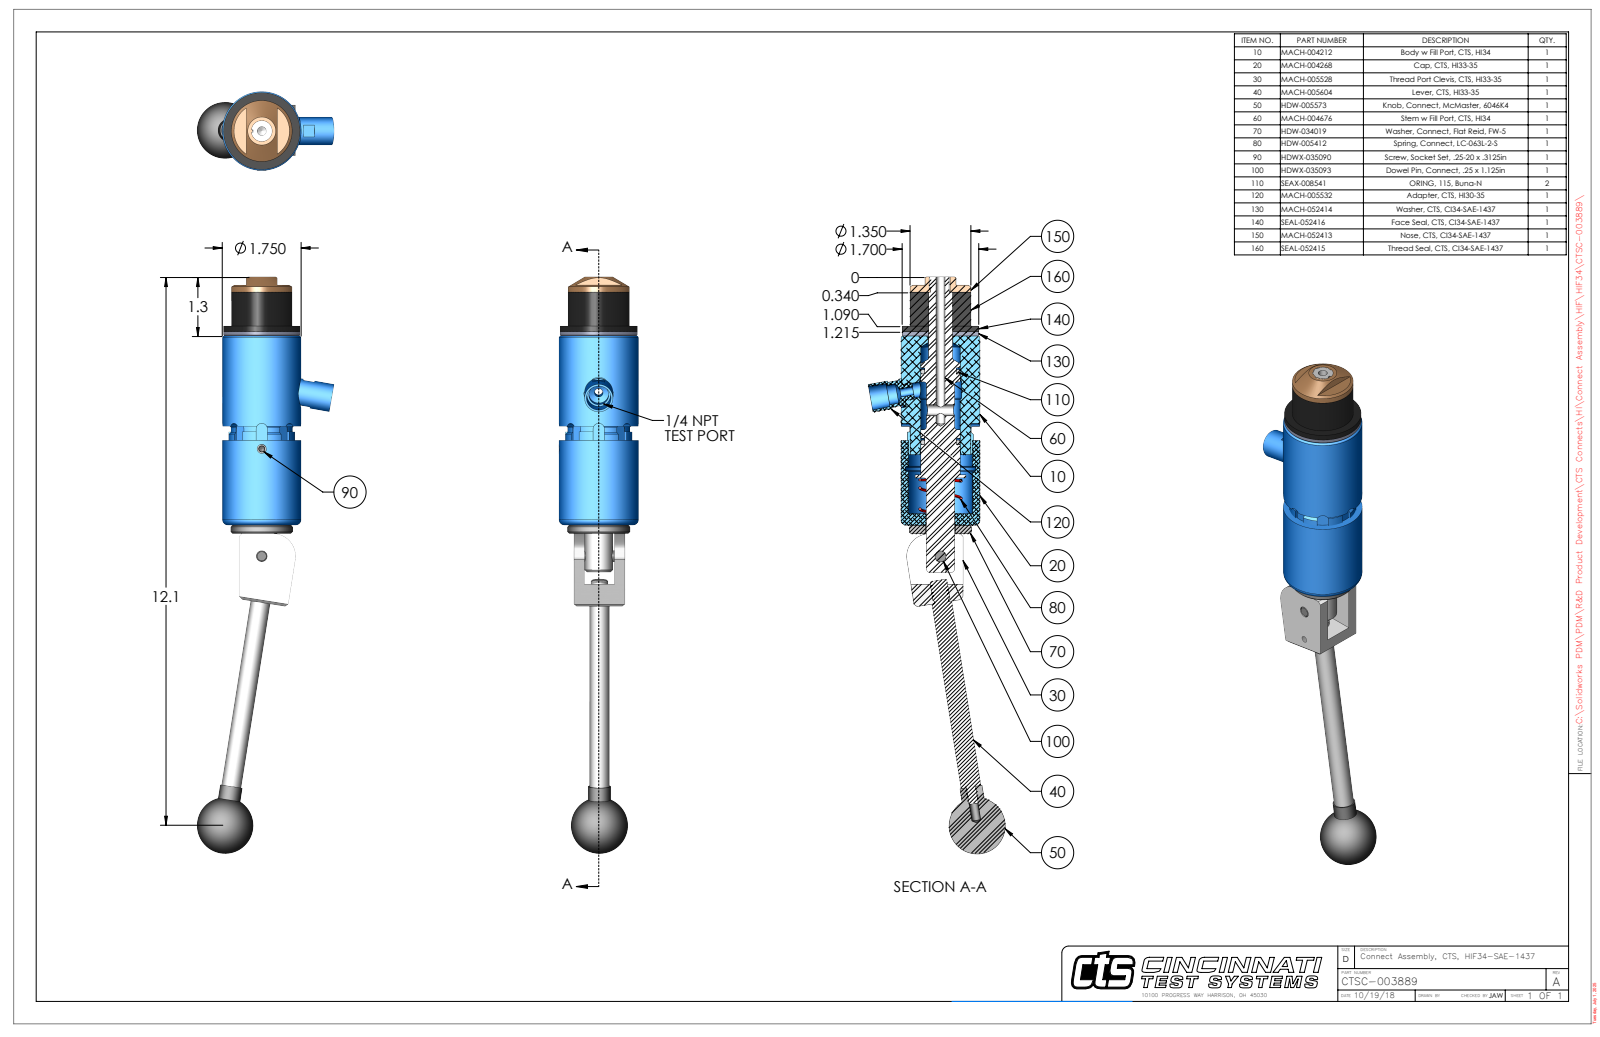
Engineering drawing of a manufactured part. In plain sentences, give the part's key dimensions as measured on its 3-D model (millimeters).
The part is named "CTSC-003889". Its 3-D file was written by "SolidWorks 2023 (AUTOMOTIVE_DESIGN)". It is 10 solids with 322 faces: 114 planar, 140 cylindrical and 68 other. Overall it measures 324.4 by 77.3 by 44.5 millimeters. Its volume is 246 000 cubic millimeters and its surface area 56 660 square millimeters. Round holes: 2 of diameter 5.1, 1 of diameter 3.8, 1 of diameter 4.7, 1 of diameter 5.2, 1 of diameter 6.3, 1 of diameter 6.4, 1 of diameter 6.4, 1 of diameter 8, 1 of diameter 8.4, 1 of diameter 10.7, 1 of diameter 11.1, 1 of diameter 13.5. Round bosses or shafts: 2 of diameter 12.7, 2 of diameter 11.2, 2 of diameter 6.4, 1 of diameter 44.5, 1 of diameter 43.2, 1 of diameter 35.1, 1 of diameter 34.3, 1 of diameter 15.9. Partial cylindrical surfaces (rounded edges, fillets, slot ends): 4 of radius 3.2, 2 of radius 0.7, 1 of radius 4.4, 1 of radius 8.4, 1 of radius 12.7, 1 of radius 17.7, 1 of radius 18, 1 of radius 18.9. The main face-to-face distances are 2.4, 5.6, 3.2, 19.1, 22.2, 24.6, 131, 112, 108.8, 106.4. The hole center spacings are 18.8, 60.4, 79.1.
